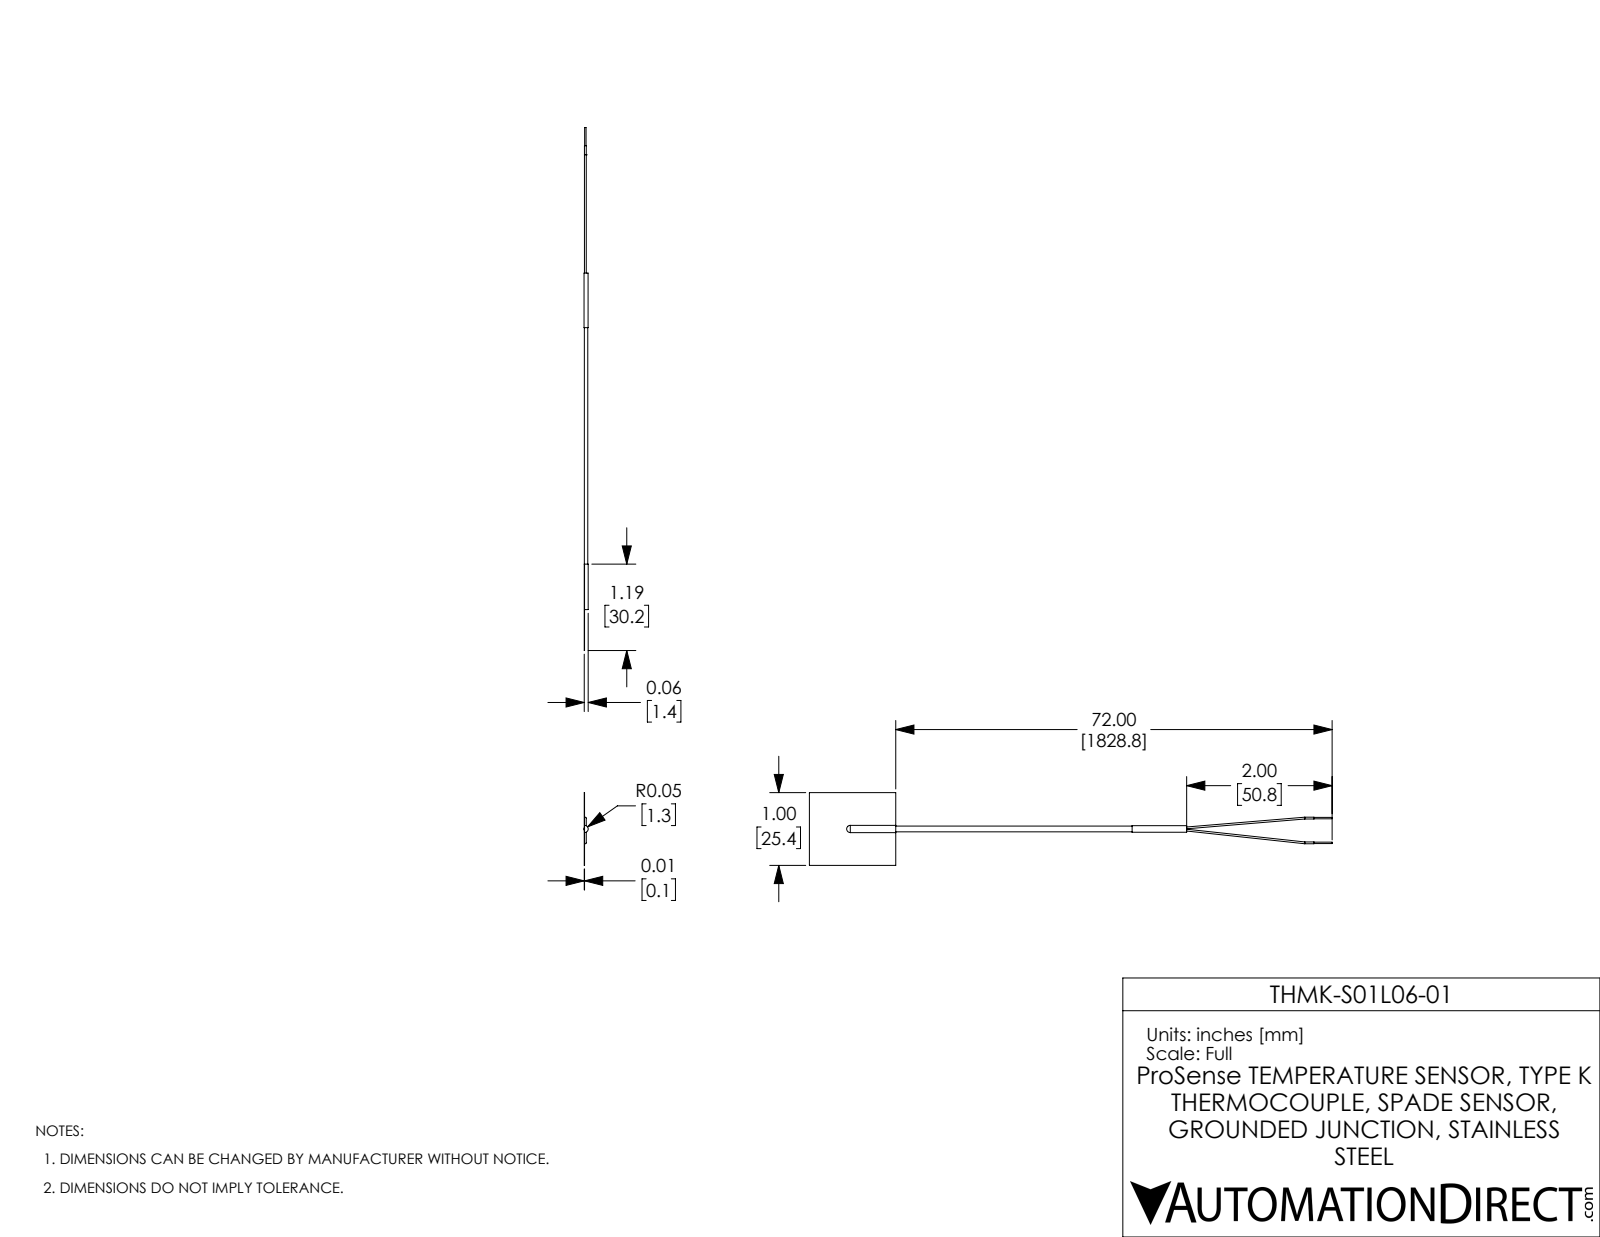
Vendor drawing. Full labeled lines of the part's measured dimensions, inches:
Part name (STEP PRODUCT): THMJ-S01L06-01 nc
STEP written by: SolidWorks 2017 (AUTOMOTIVE_DESIGN)
Units: inches
Bodies: 3 solids, 37 faces (14 planar, 14 cylindrical, 9 other)
Overall size (bounding box): 7.188 × 1 × 0.057
Volume: 0.024 in³ · Surface area: 3.667 in²
Round bosses / shafts (diameter × count): ⌀0.025 ×4, ⌀0.02 ×2
Partial cylindrical surfaces — rounded edges, fillets, slot ends (radius × count): R0.05 ×1
Main face-to-face distances: 1, 1.187, 4, 5.187, 0.25, 0.5, 3.5, 4.687, 2.5, 0.75
